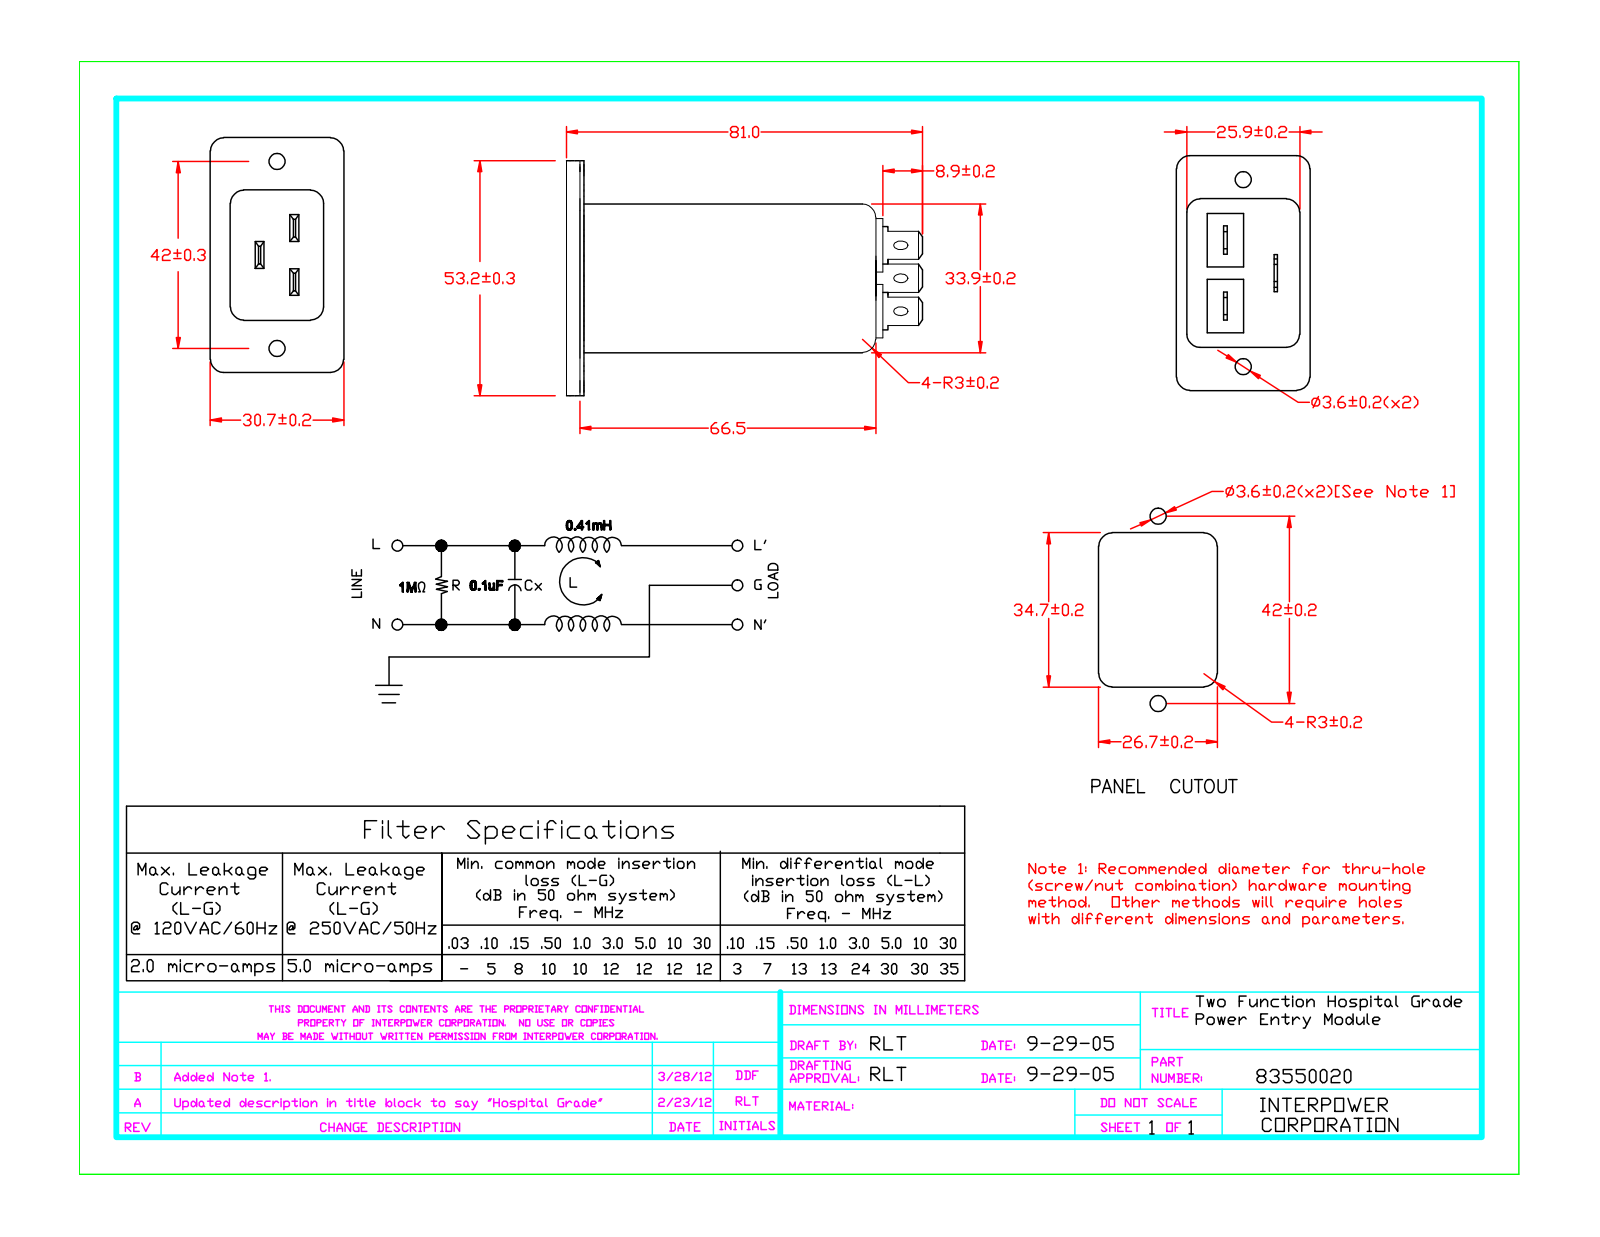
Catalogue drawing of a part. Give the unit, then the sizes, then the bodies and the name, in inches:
Units: inches
Overall size (bounding box): 3.189 × 2.094 × 1.209
Round holes (diameter × count): ⌀0.136 ×2
Partial cylindrical surfaces — rounded edges, fillets, slot ends (radius × count): R0.118 ×12, R0.01 ×8, R0.197 ×8
Main face-to-face distances: 1.02, 1.335, 0.096, 0.923, 0.157, 0.138, 0.02, 0.028, 0.048, 0.185
Hole centre spacings: 1.654
Volume: 3.245 in³ · Surface area: 24.31 in²
Bodies: 1 solid, 156 faces (94 planar, 40 cylindrical, 22 other)
Part name (STEP PRODUCT): 83550020
STEP written by: SolidWorks 2007 (CONFIG_CONTROL_DESIGN)
